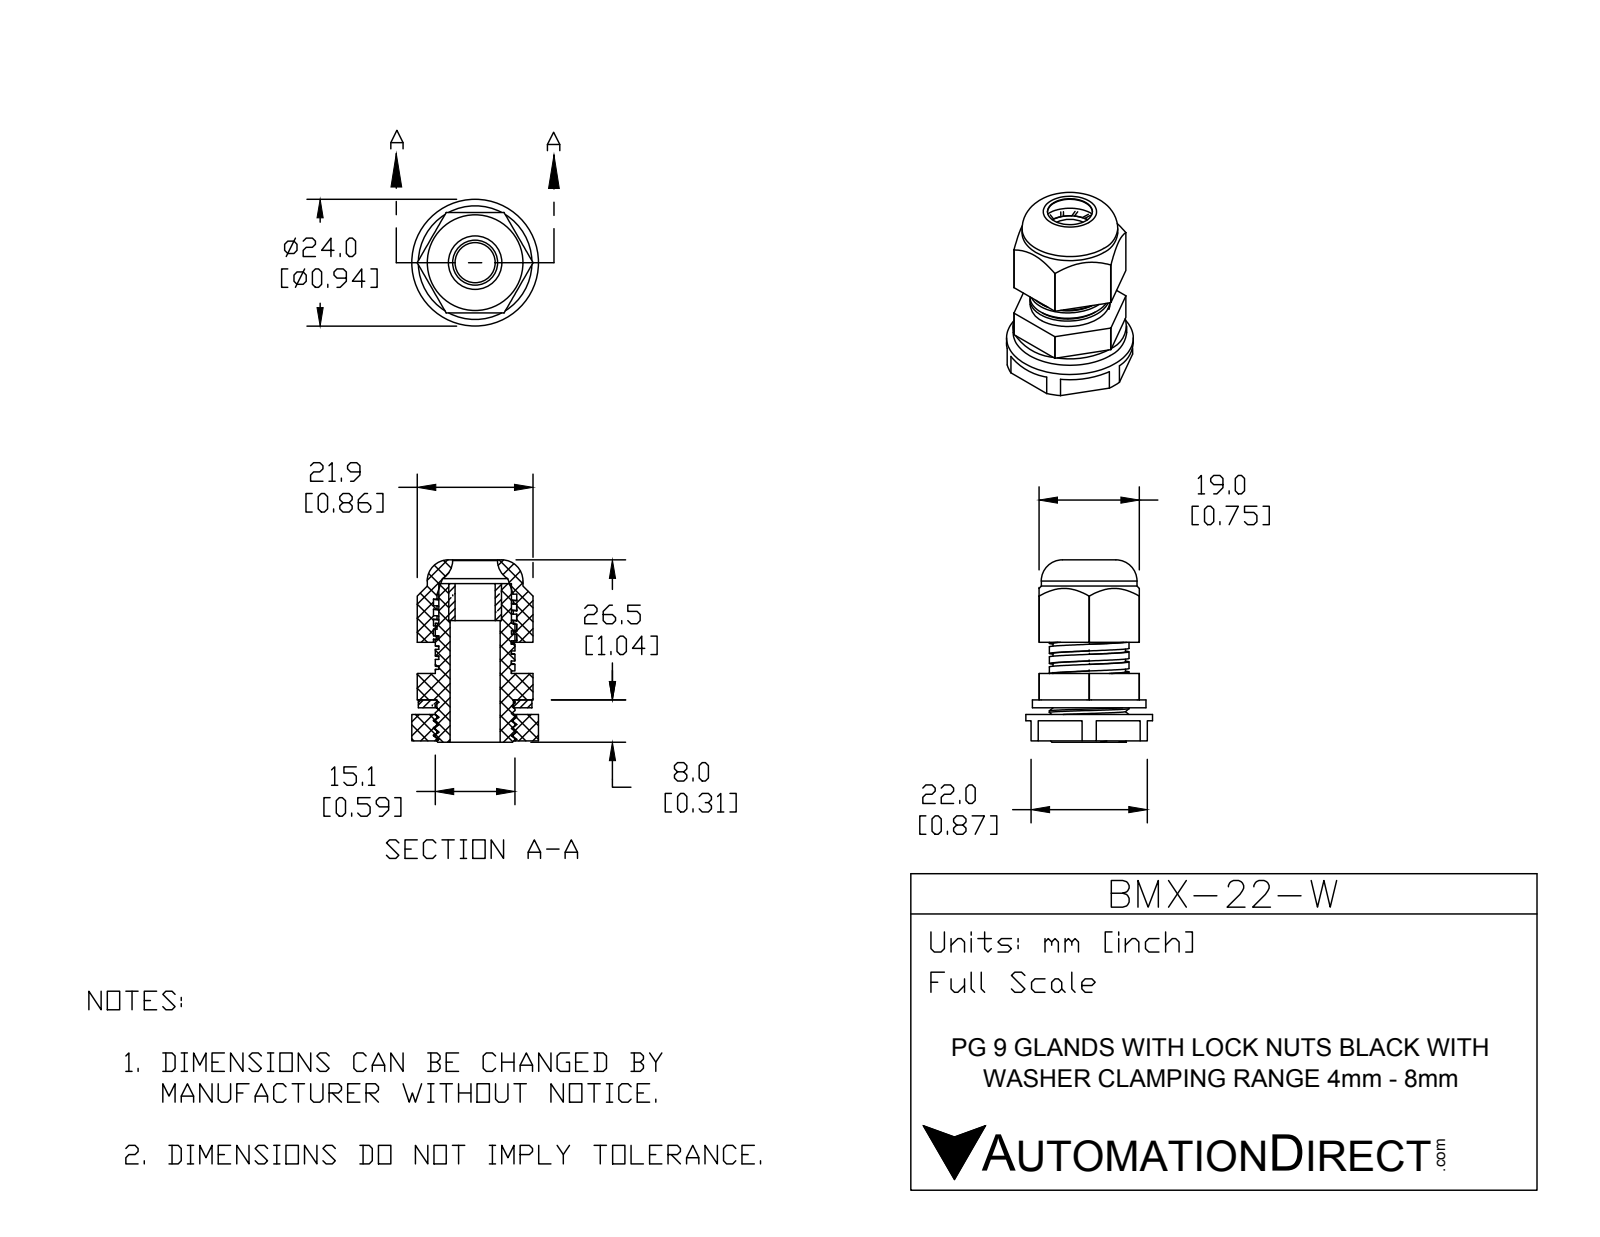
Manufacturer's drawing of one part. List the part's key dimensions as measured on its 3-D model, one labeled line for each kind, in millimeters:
Part name (STEP PRODUCT): BMX-22-W
STEP written by: SolidWorks 2015 (CONFIG_CONTROL_DESIGN)
Units: millimetres
Bodies: 5 solids, 198 faces (99 planar, 76 cylindrical, 23 other)
Overall size (bounding box): 34.5 × 24 × 24
Volume: 7 155 mm³ · Surface area: 8 073 mm²
Round holes (diameter × count): ⌀7.6 ×1, ⌀8.5 ×1, ⌀9.5 ×1, ⌀10 ×1, ⌀14.43 ×1, ⌀14.5 ×1
Round bosses / shafts (diameter × count): ⌀24 ×1, ⌀21.5 ×1, ⌀18.1 ×1, ⌀15.1 ×1, ⌀13.75 ×1
Partial cylindrical surfaces — rounded edges, fillets, slot ends (radius × count): R10.95 ×1
Main face-to-face distances: 19, 1.5, 7.5, 5, 0.5, 2.5, 22, 6.5, 20.5, 6
